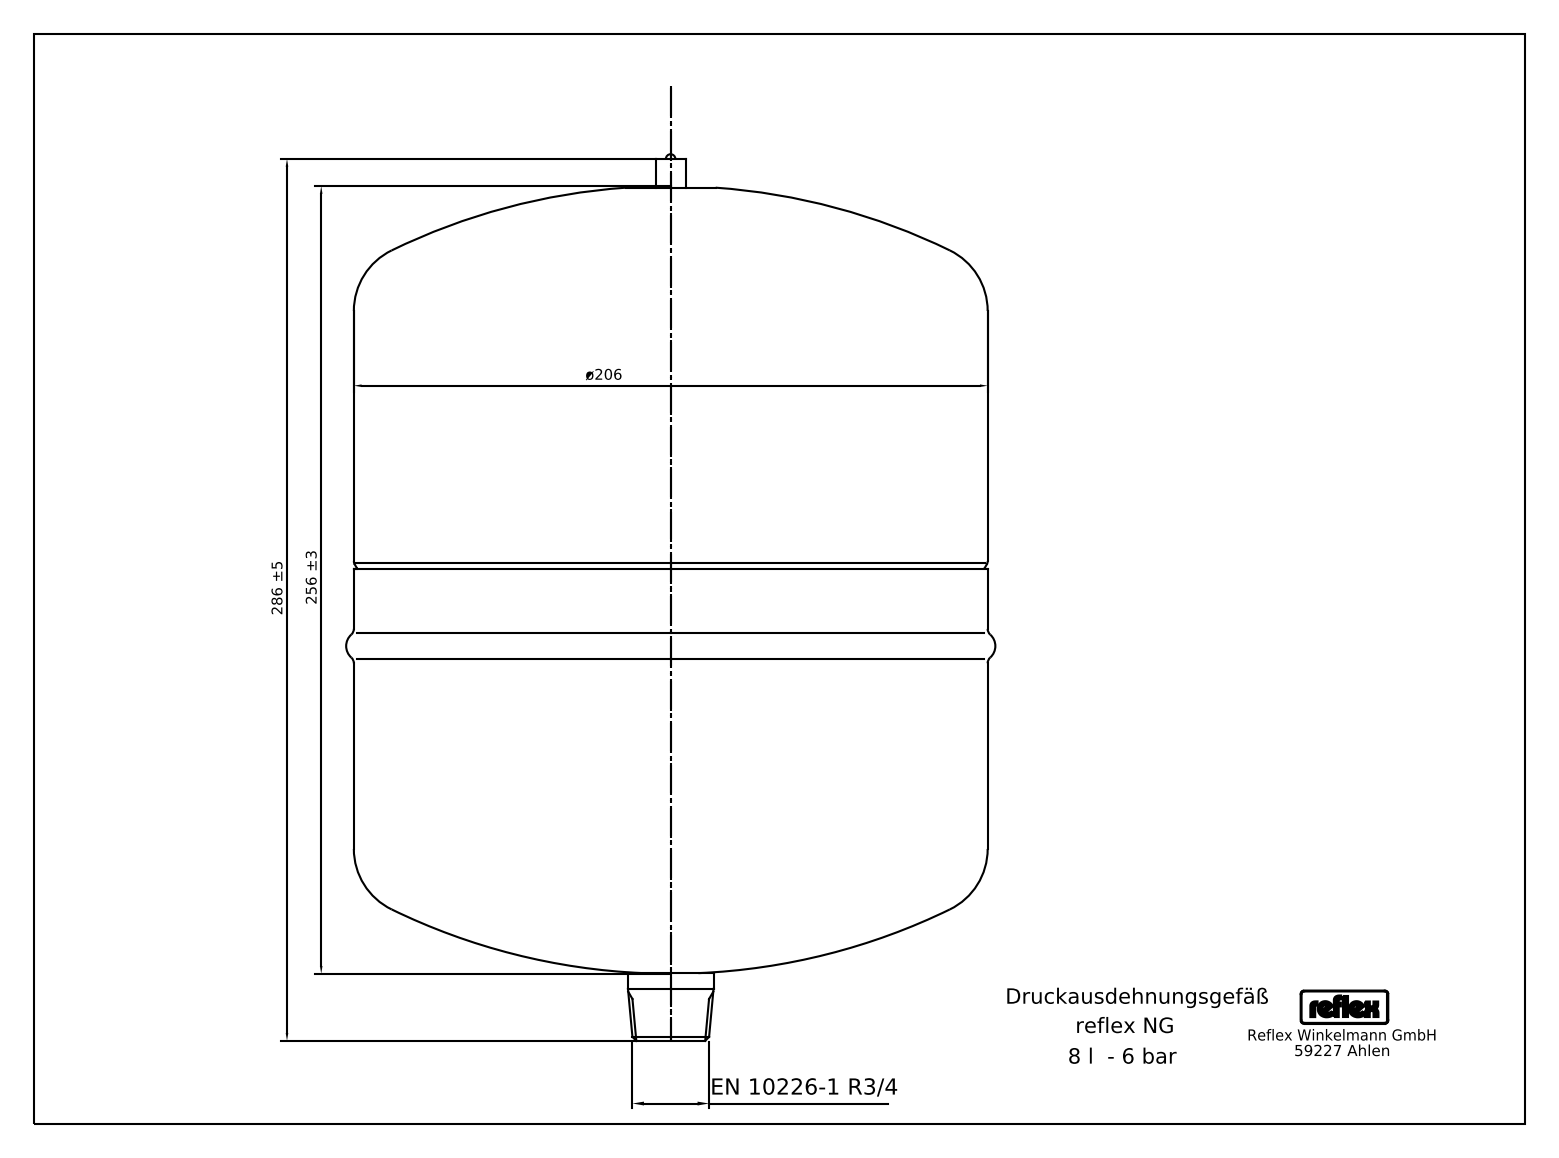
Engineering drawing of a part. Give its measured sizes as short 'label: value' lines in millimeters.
name: reflex_NG8
written by: CATIA V5 STEP AP214 (AUTOMOTIVE_DESIGN)
unit: mm
bodies: 1 solid, 34 faces (4 planar, 10 cylindrical, 20 other)
size: 286 × 211 × 211
volume: 7 595 000 mm³; area: 202 213 mm²
bosses: 1× ⌀206, 1× ⌀28, 1× ⌀10
face distances: 122, 154, 276, 285, 131, 9
